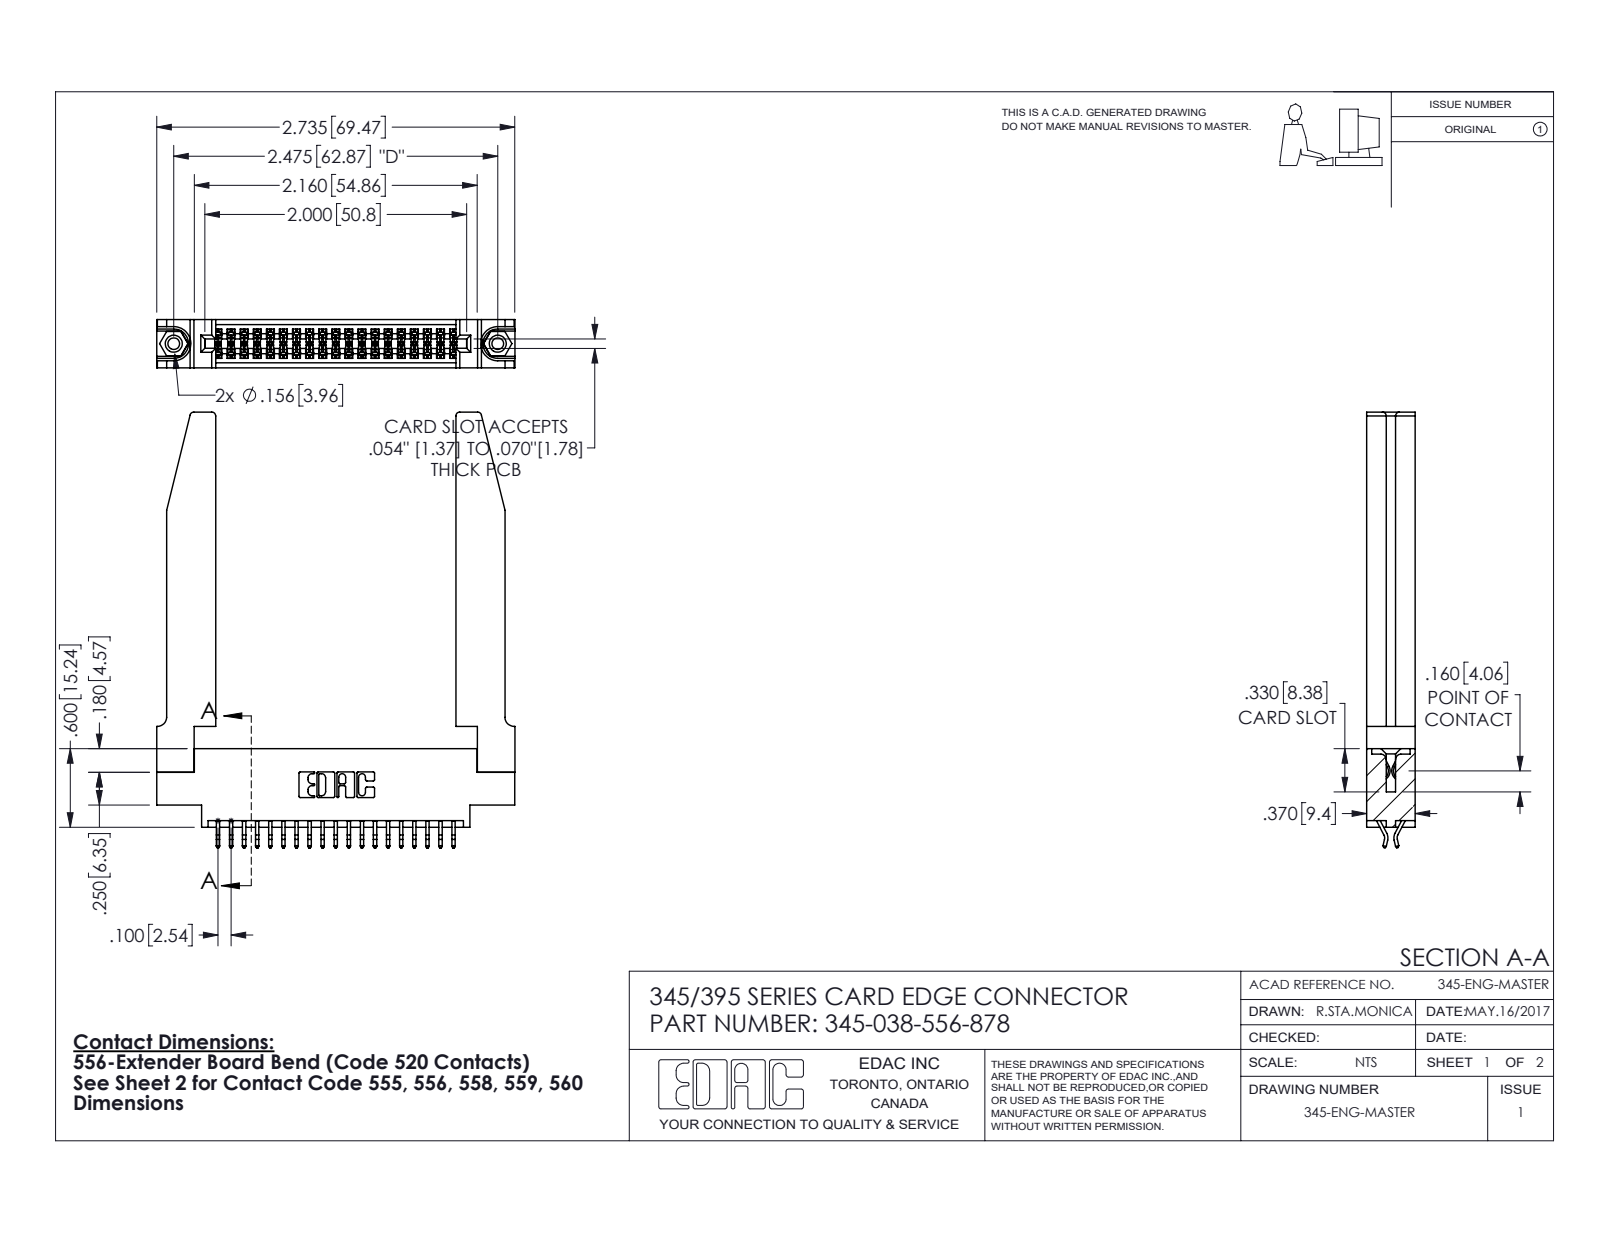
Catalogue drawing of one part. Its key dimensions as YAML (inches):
part_name: "345-250-001_345-250-001-102; 345-220-078_345-220-078; 345-038-556-878; 345-292-001_556 Tail (+1 more)"
step_written_by: "SolidWorks 2016 (CONFIG_CONTROL_DESIGN)"
units: inches
bodies: {solids: 43, faces: 2492, planar: 1632, cylindrical: 808, other: 52}
overall_size: [3.327, 2.736, 0.37]
volume: 0.866
surface_area: 24.79
round_holes:
  - {diameter: 0.089, count: 2}
  - {diameter: 0.125, count: 2}
  - {diameter: 0.156, count: 2}
  - {diameter: 0.064, count: 1}
round_bosses_or_shafts:
  - {diameter: 0.155, count: 2}
partial_cylinders:
  - {radius: 0.006, count: 57}
  - {radius: 0.01, count: 22}
  - {radius: 0.03, count: 8}
  - {radius: 0.007, count: 6}
  - {radius: 0.031, count: 6}
  - {radius: 0.026, count: 3}
  - {radius: 0.01, count: 2}
  - {radius: 0.014, count: 2}
face_to_face_distances: [0.37, 0.072, 0.298, 0.025, 0.2, 0.148, 0.15, 0.098, 0.272, 0.225]
hole_center_spacings: [0.27, 2.241, 2.475]
